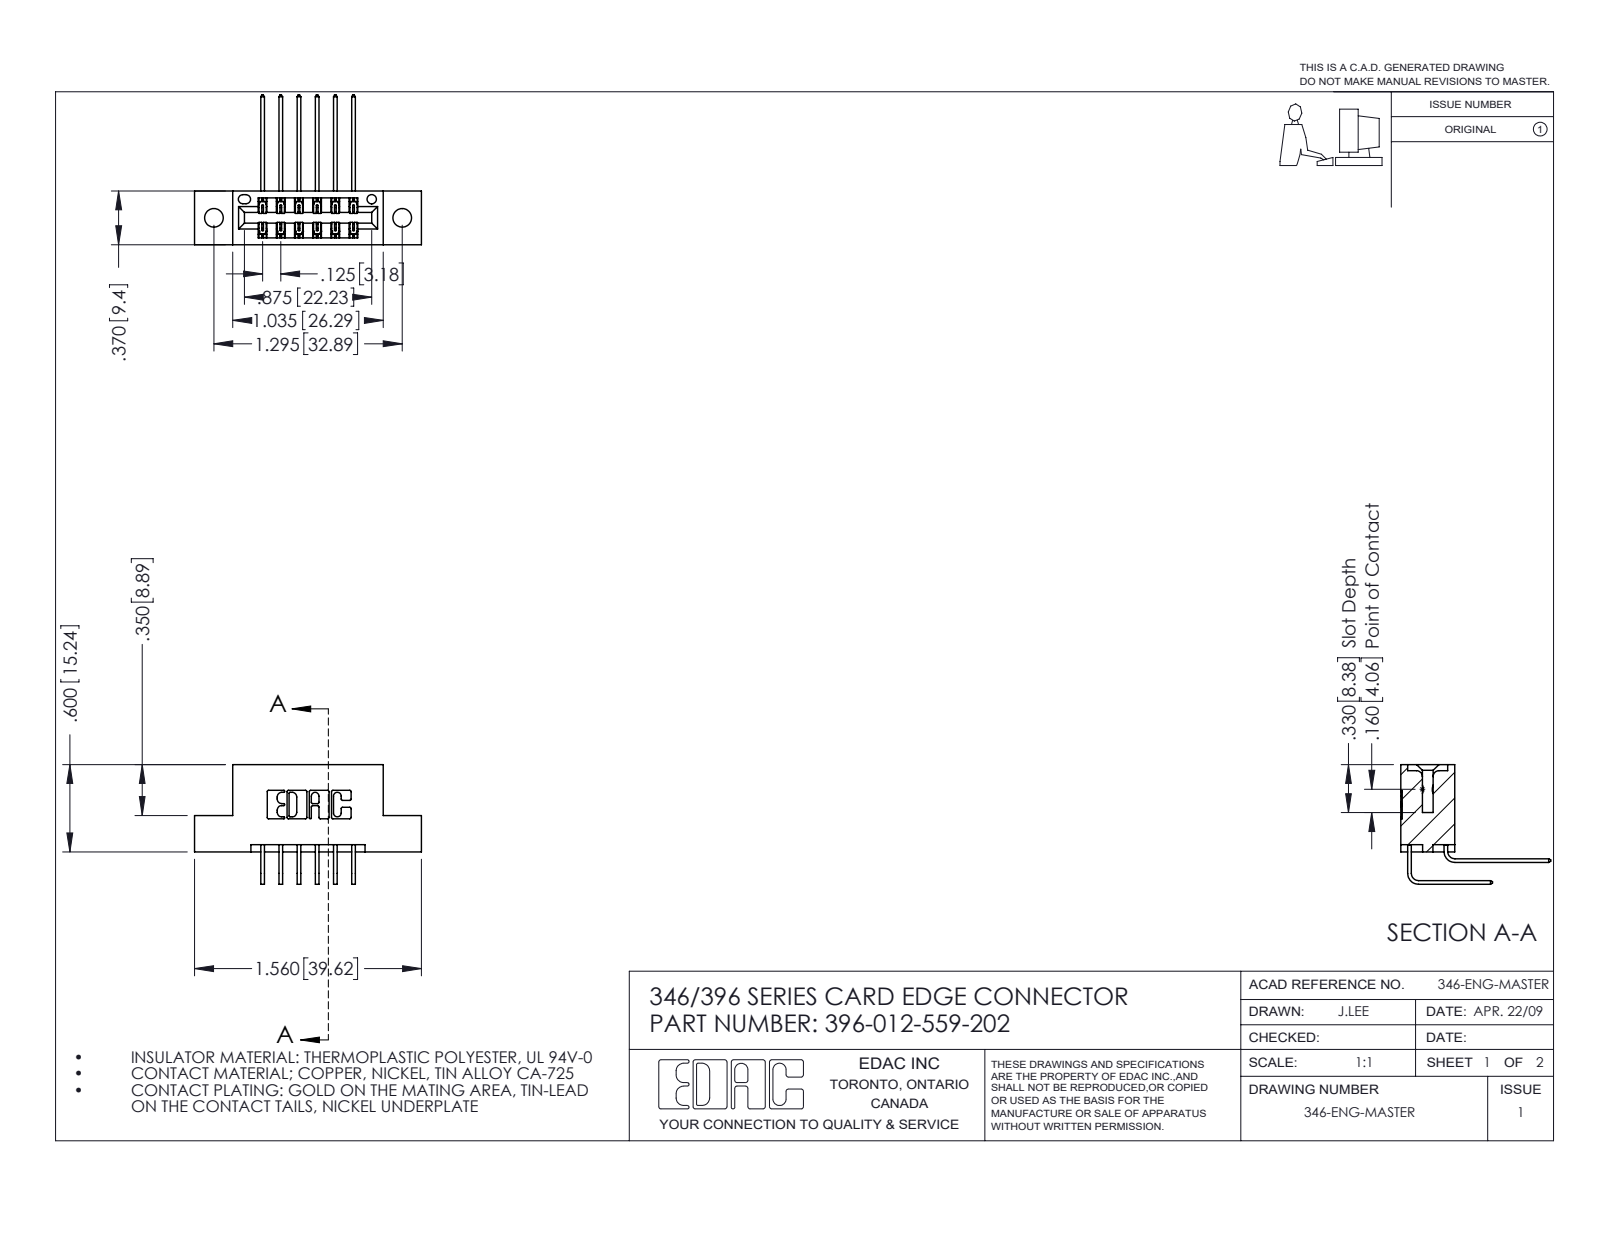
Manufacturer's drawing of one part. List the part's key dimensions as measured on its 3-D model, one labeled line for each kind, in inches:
Part name (STEP PRODUCT): 396-012-559-202; 345-292-001_559 Tail - 2; 345-292-001_558 559 Tail - 1; 346 Part_Flush Mounting Lugs - 0.128 Dia
STEP written by: SolidWorks 2016 (CONFIG_CONTROL_DESIGN)
Units: inches
Bodies: 13 solids, 770 faces (520 planar, 250 cylindrical, 0 other)
Overall size (bounding box): 1.56 × 1.03 × 0.823
Volume: 0.221 in³ · Surface area: 6.926 in²
Round holes (diameter × count): ⌀0.128 ×2, ⌀0.064 ×1
Partial cylindrical surfaces — rounded edges, fillets, slot ends (radius × count): R0.01 ×22, R0.006 ×18, R0.007 ×6, R0.031 ×6, R0.026 ×3, R0.014 ×2, R0.022 ×2, R0.024 ×2
Main face-to-face distances: 0.25, 0.048, 0.322, 0.37, 0.025, 0.298, 0.072, 0.125, 0.148, 0.222
Hole centre spacings: 0.246, 1.092, 1.295
